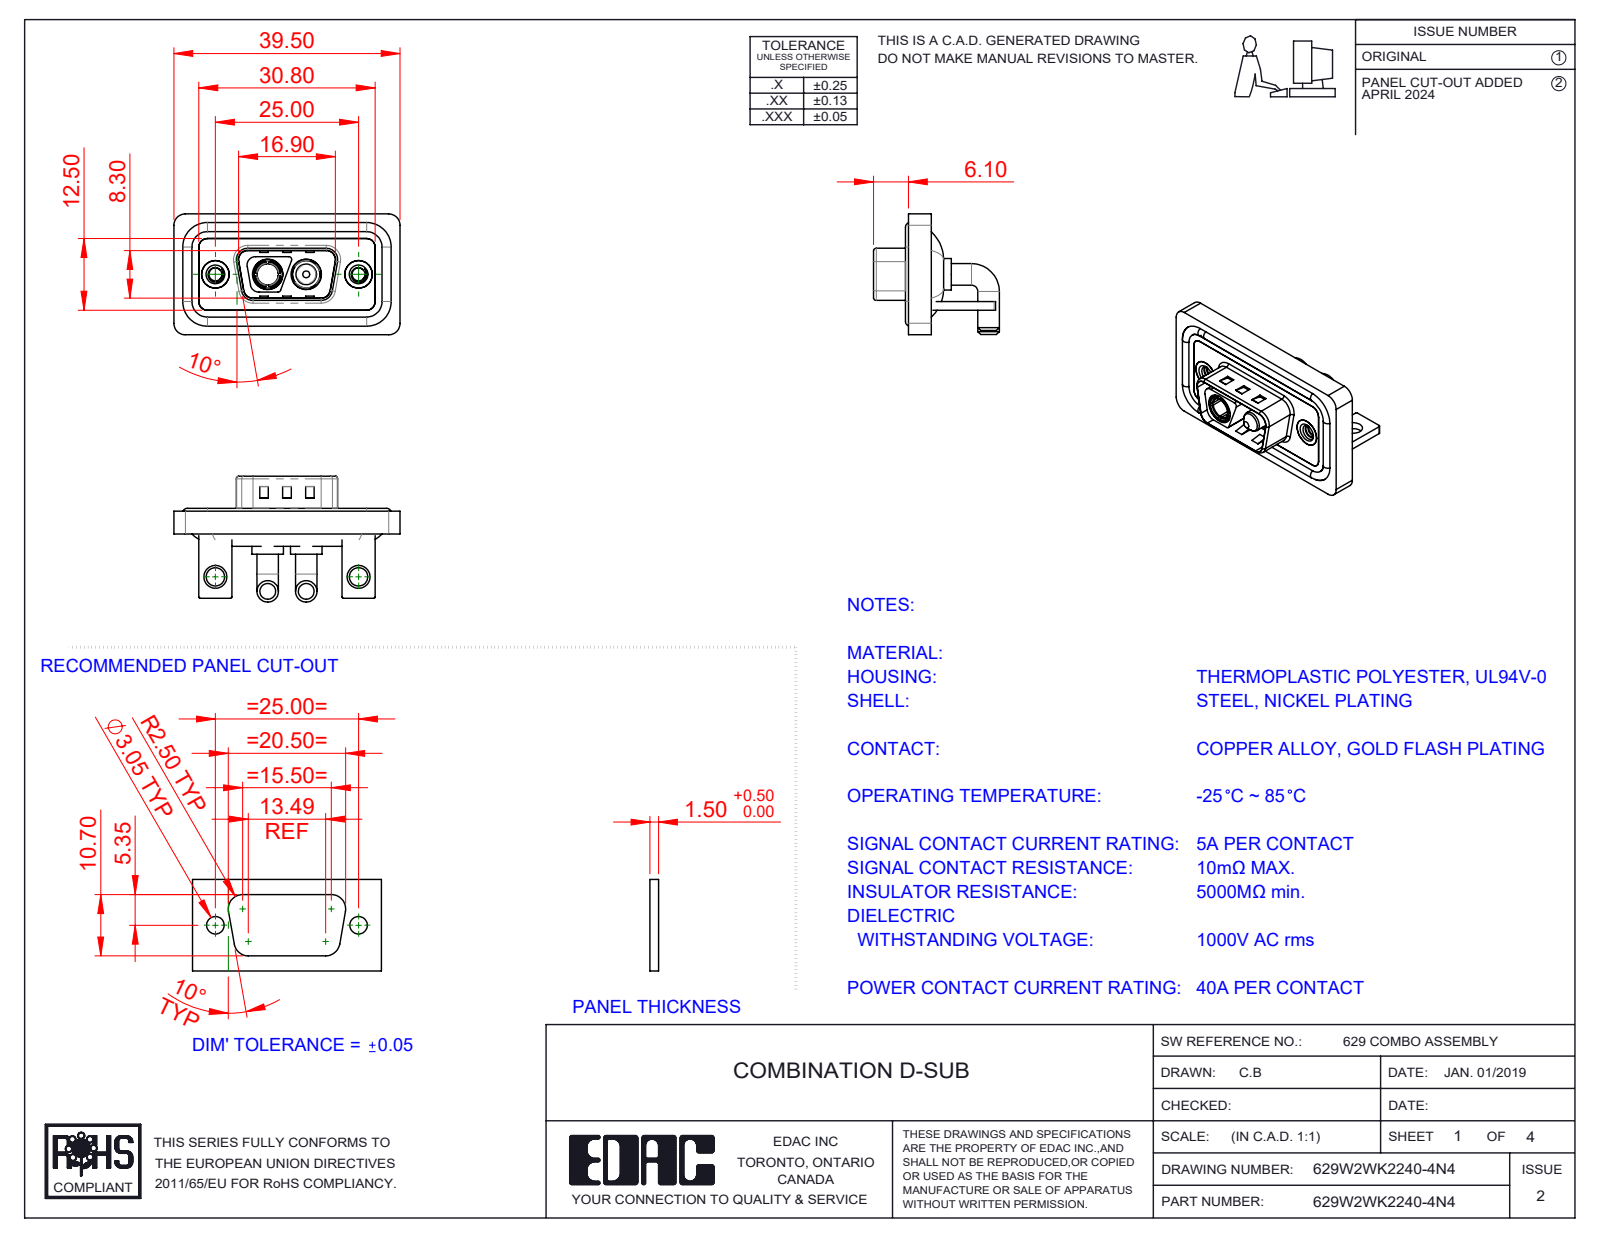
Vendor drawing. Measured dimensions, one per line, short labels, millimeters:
name: 629W2WK2240-4N4; 629Combo Threaded Rivet_3; Power Socket_40A RA; Power Pin_40A RA (+5 more)
written by: SolidWorks 2023 (CONFIG_CONTROL_DESIGN)
unit: mm
bodies: 13 solids, 582 faces (209 planar, 249 cylindrical, 124 other)
size: 39.5 × 21.98 × 21.1
volume: 5 109 mm³; area: 8 209 mm²
holes: 2× ⌀2.26, 2× ⌀3.2, 2× ⌀4, 2× ⌀4.8, 2× ⌀4.85, 2× ⌀5, 2× ⌀5.3, 1× ⌀3.7
bosses: 4× ⌀3.75, 4× ⌀1.6, 2× ⌀5.5, 2× ⌀5.2, 2× ⌀4.9, 2× ⌀4.75, 1× ⌀4.96, 1× ⌀3.6
rounds: 20× R1.5, 19× R2, 16× R0.25, 11× R0.5, 8× R1.6, 4× R0.6, 4× R0.65, 4× R0.9
face distances: 0.4, 1.5, 2.9, 0.8, 1.1, 1.2, 2.1, 1.6, 3.7, 2.5
hole spacings: 9.14, 15.86, 25, 6.72
